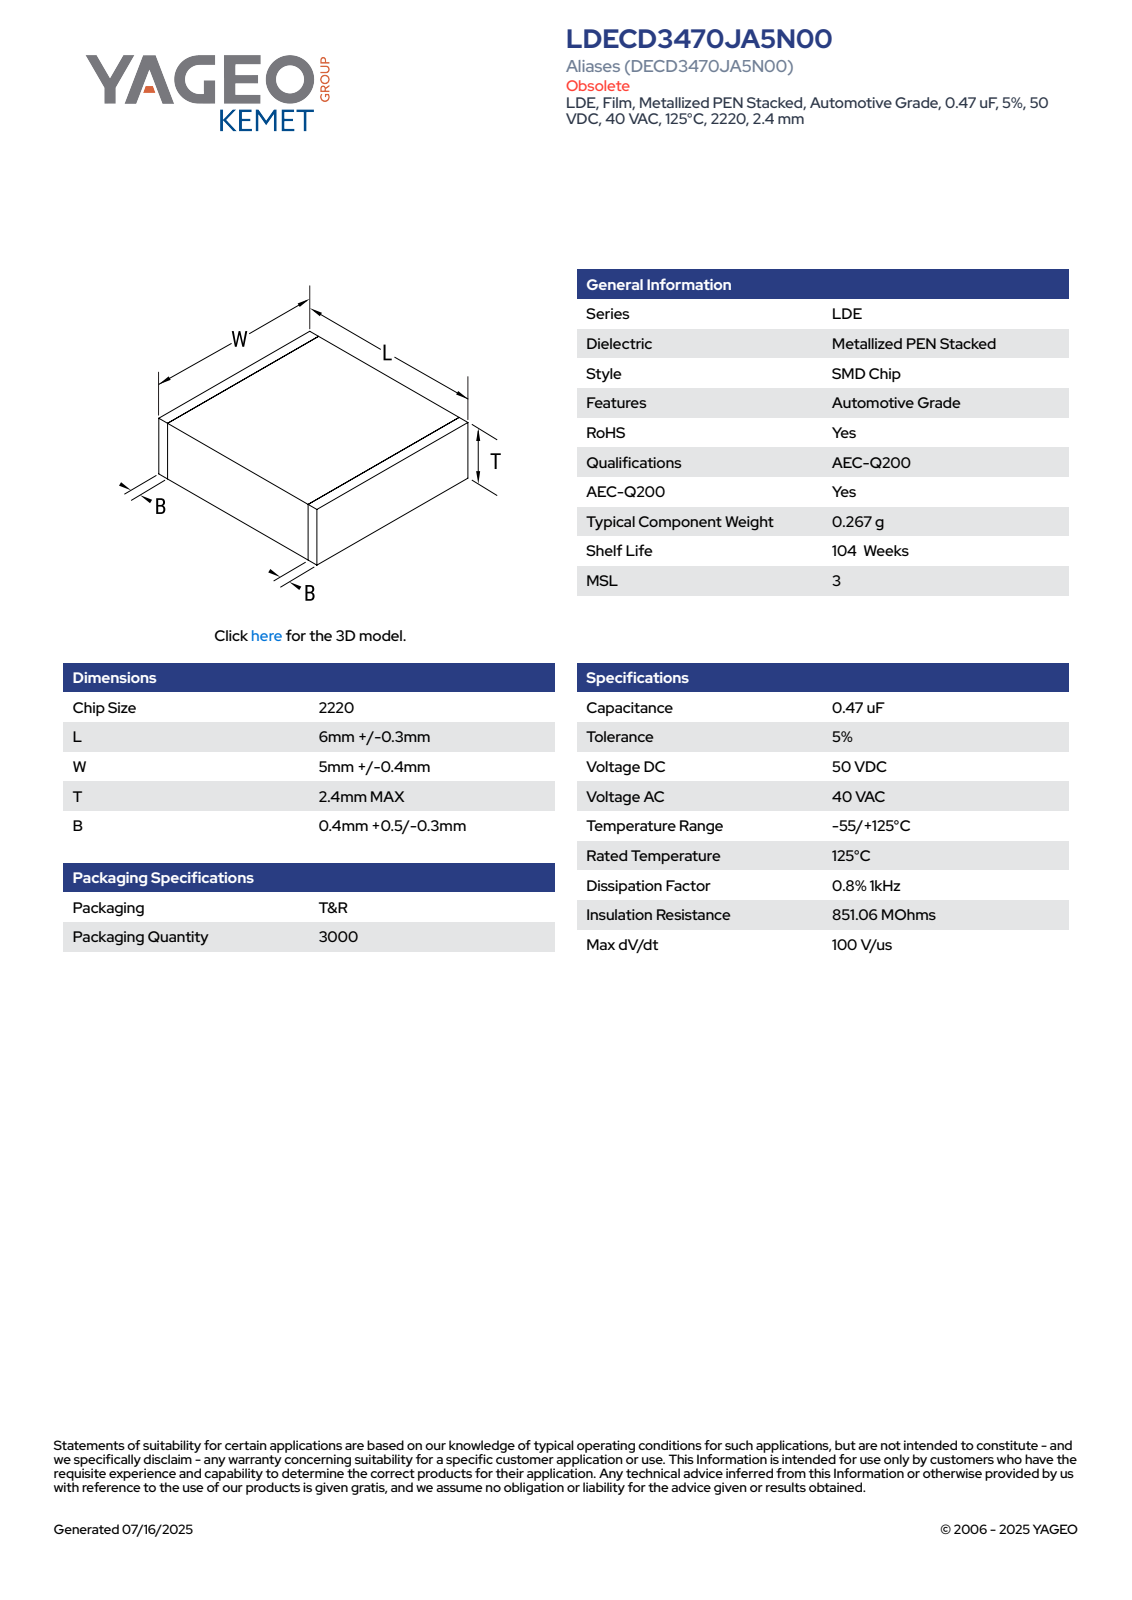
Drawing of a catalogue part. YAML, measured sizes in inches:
part_name: "CFS_LDELDB_2220_L6.3W5.4T2.4B0.9"
step_written_by: "SolidWorks 2020 (AUTOMOTIVE_DESIGN)"
units: inches
bodies: {solids: 4, faces: 73, planar: 73, cylindrical: 0, other: 0}
overall_size: [0.248, 0.213, 0.094]
volume: 0.005
surface_area: 0.195
face_to_face_distances: [0.094, 0.248, 0.212, 0.094, 0.094, 0.212, 0.213, 0.02, 0.228, 0.209]
